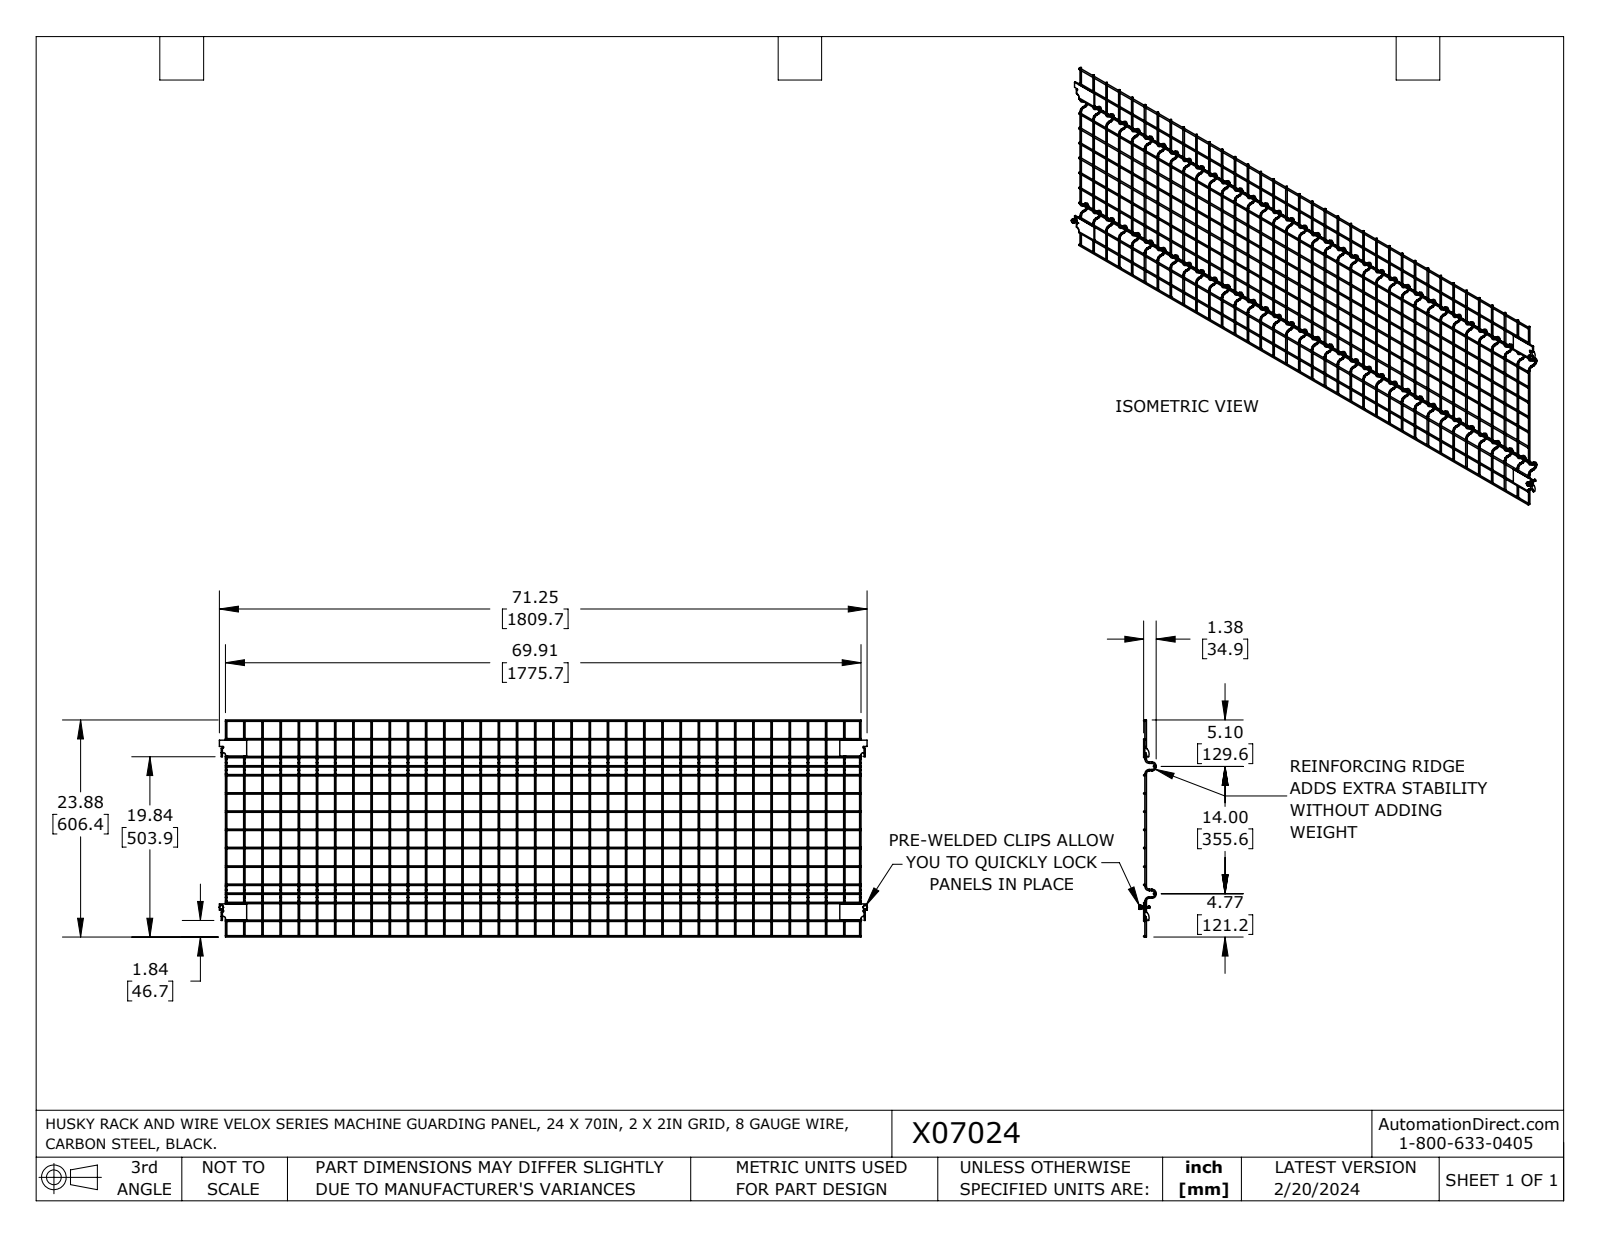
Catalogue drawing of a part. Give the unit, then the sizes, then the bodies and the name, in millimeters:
Units: millimetres
Overall size (bounding box): 1811.4 × 606.4 × 47.1
Round holes (diameter × count): ⌀5.1 ×2, ⌀6.4 ×2
Round bosses / shafts (diameter × count): ⌀4.1 ×231, ⌀9.9 ×2, ⌀6.2 ×2, ⌀4.7 ×2
Partial cylindrical surfaces — rounded edges, fillets, slot ends (radius × count): R2.5 ×4, R5.5 ×4, R0.2 ×2, R1.7 ×2, R3.4 ×2, R6.4 ×2, R22 ×2
Main face-to-face distances: 3.4, 3.2, 71.1, 1728.4, 457.2, 457.2, 92.7, 549.9, 606.4, 513.7
Hole centre spacings: 1798.5
Volume: 709 400 mm³ · Surface area: 687 100 mm²
Bodies: 59 solids, 869 faces (182 planar, 375 cylindrical, 312 other)
Part name (STEP PRODUCT): X07024
STEP written by: SolidWorks 2023 (AUTOMOTIVE_DESIGN)
